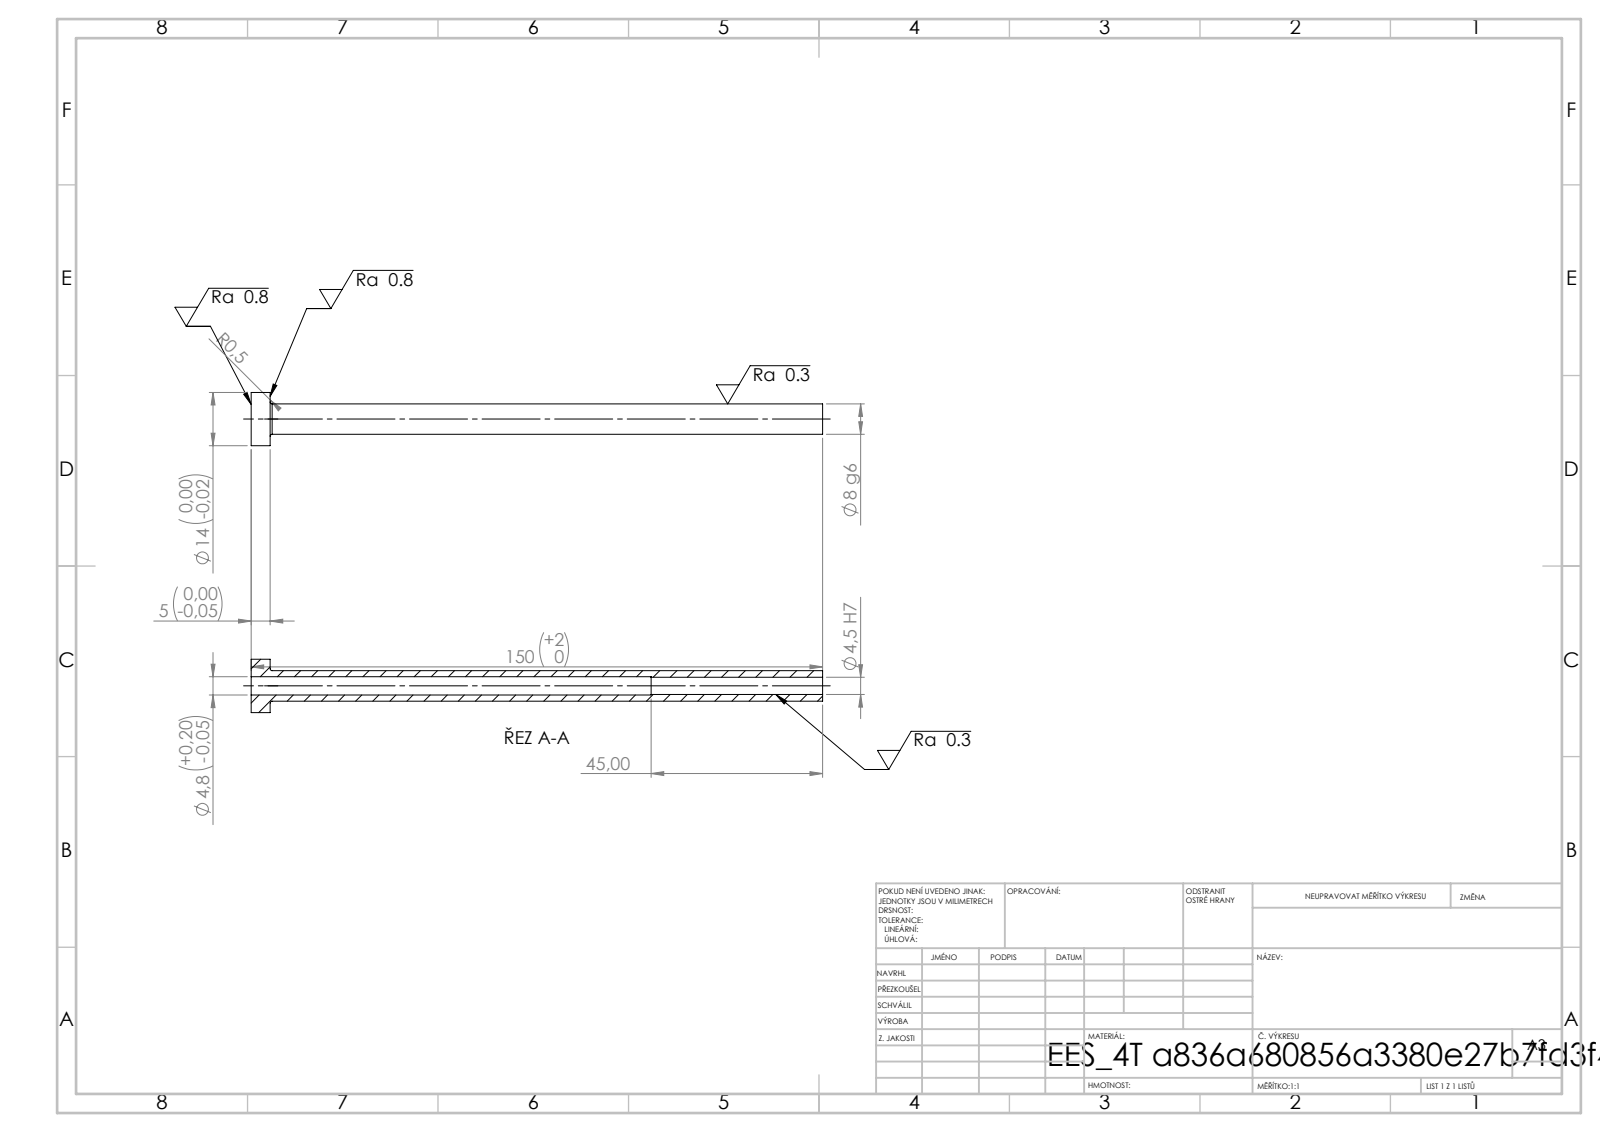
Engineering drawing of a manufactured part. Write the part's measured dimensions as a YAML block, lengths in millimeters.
step_written_by: "SolidWorks 2019 (CONFIG_CONTROL_DESIGN)"
units: millimeters
bodies: {solids: 1, faces: 14, planar: 4, cylindrical: 8, other: 2}
overall_size: [150, 14, 14]
volume: 5444
surface_area: 6354
round_holes:
  - {diameter: 4.5, count: 1}
  - {diameter: 4.8, count: 1}
round_bosses_or_shafts:
  - {diameter: 14, count: 1}
  - {diameter: 8, count: 1}
face_to_face_distances: [5, 150, 145, 105, 100, 45]
